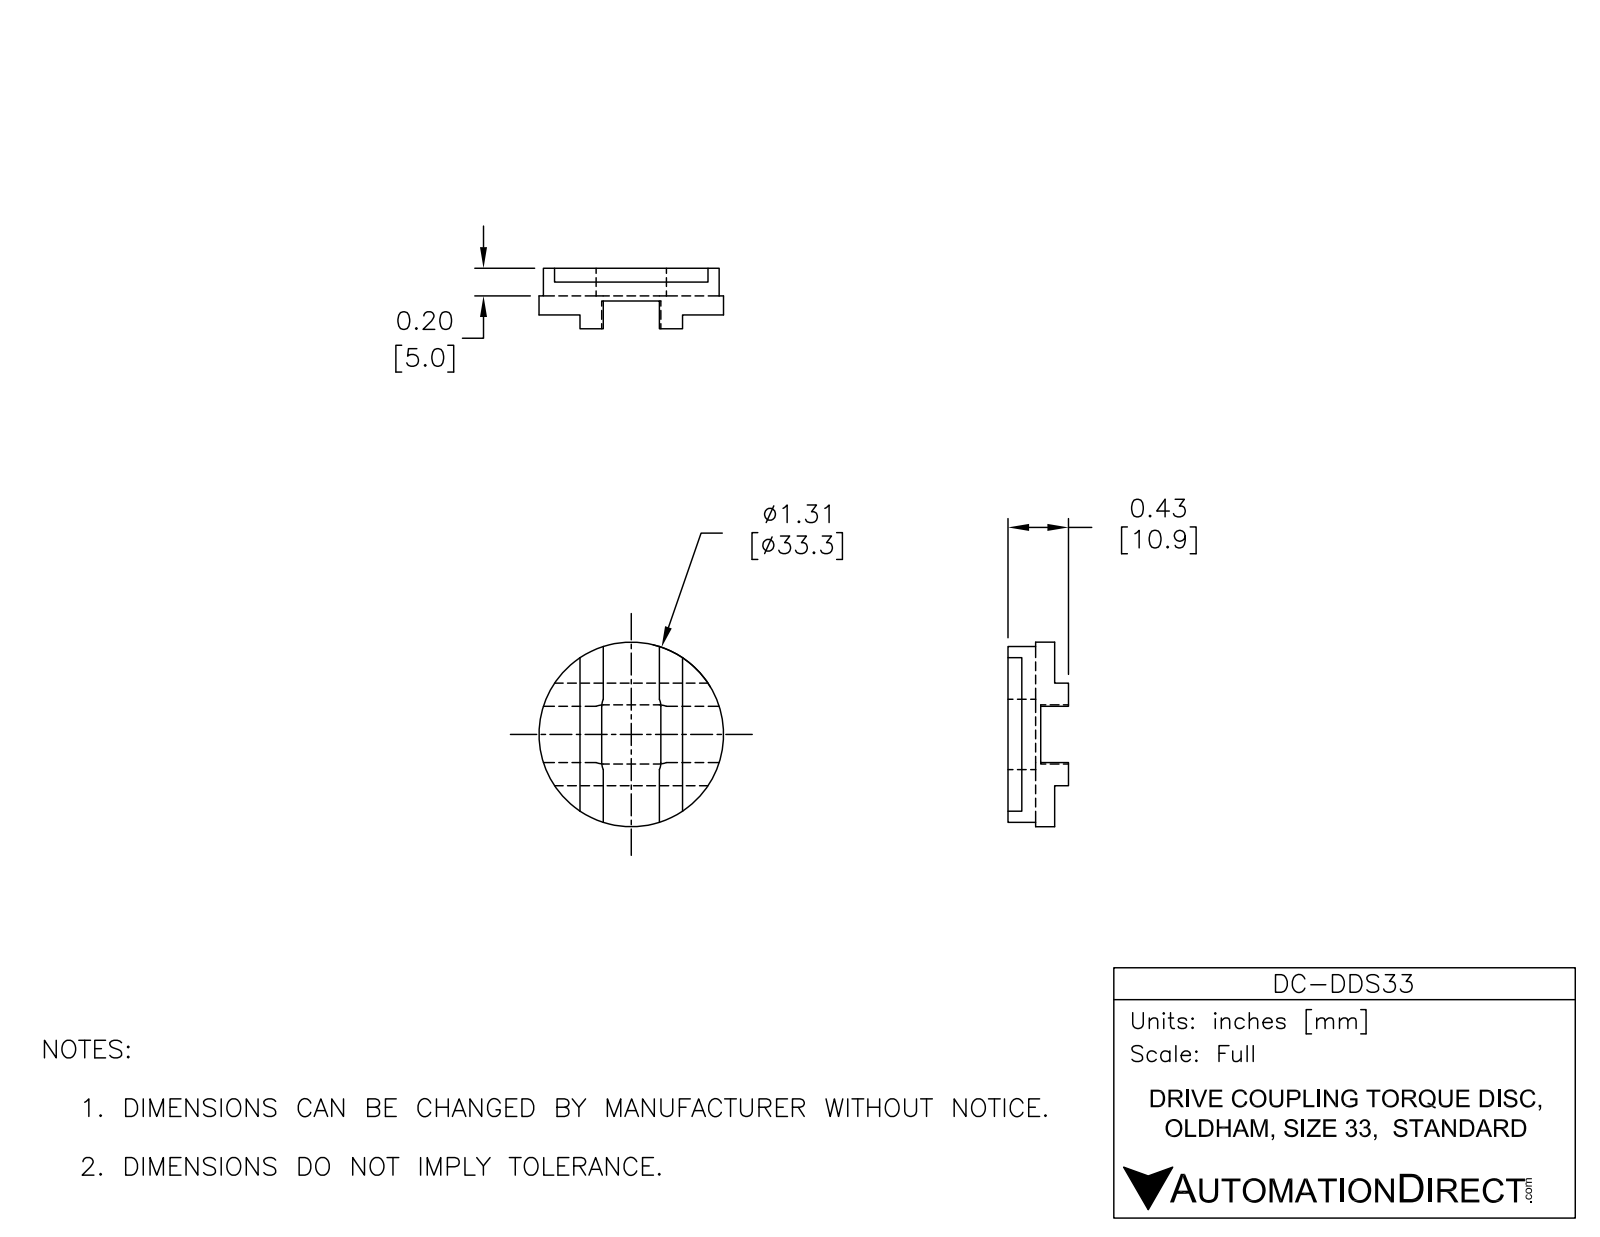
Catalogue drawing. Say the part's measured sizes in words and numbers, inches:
The part is named "DC-DDS33". Its 3-D file was written by "SolidWorks 2015 (AUTOMOTIVE_DESIGN)". It is 1 solid with 36 faces: 30 planar, 6 cylindrical and 0 other. Overall it measures 1.311 by 1.311 by 0.43 inches. Its volume is 0.286 cubic inches and its surface area 5.067 square inches. Round bosses or shafts: 1 of diameter 1.311. Partial cylindrical surfaces (rounded edges, fillets, slot ends): 4 of radius 0.125. The main face-to-face distances are 0.098, 0.233, 0.135, 0.197, 0.331, 0.036, 0.165, 0.564, 0.43, 0.574.
